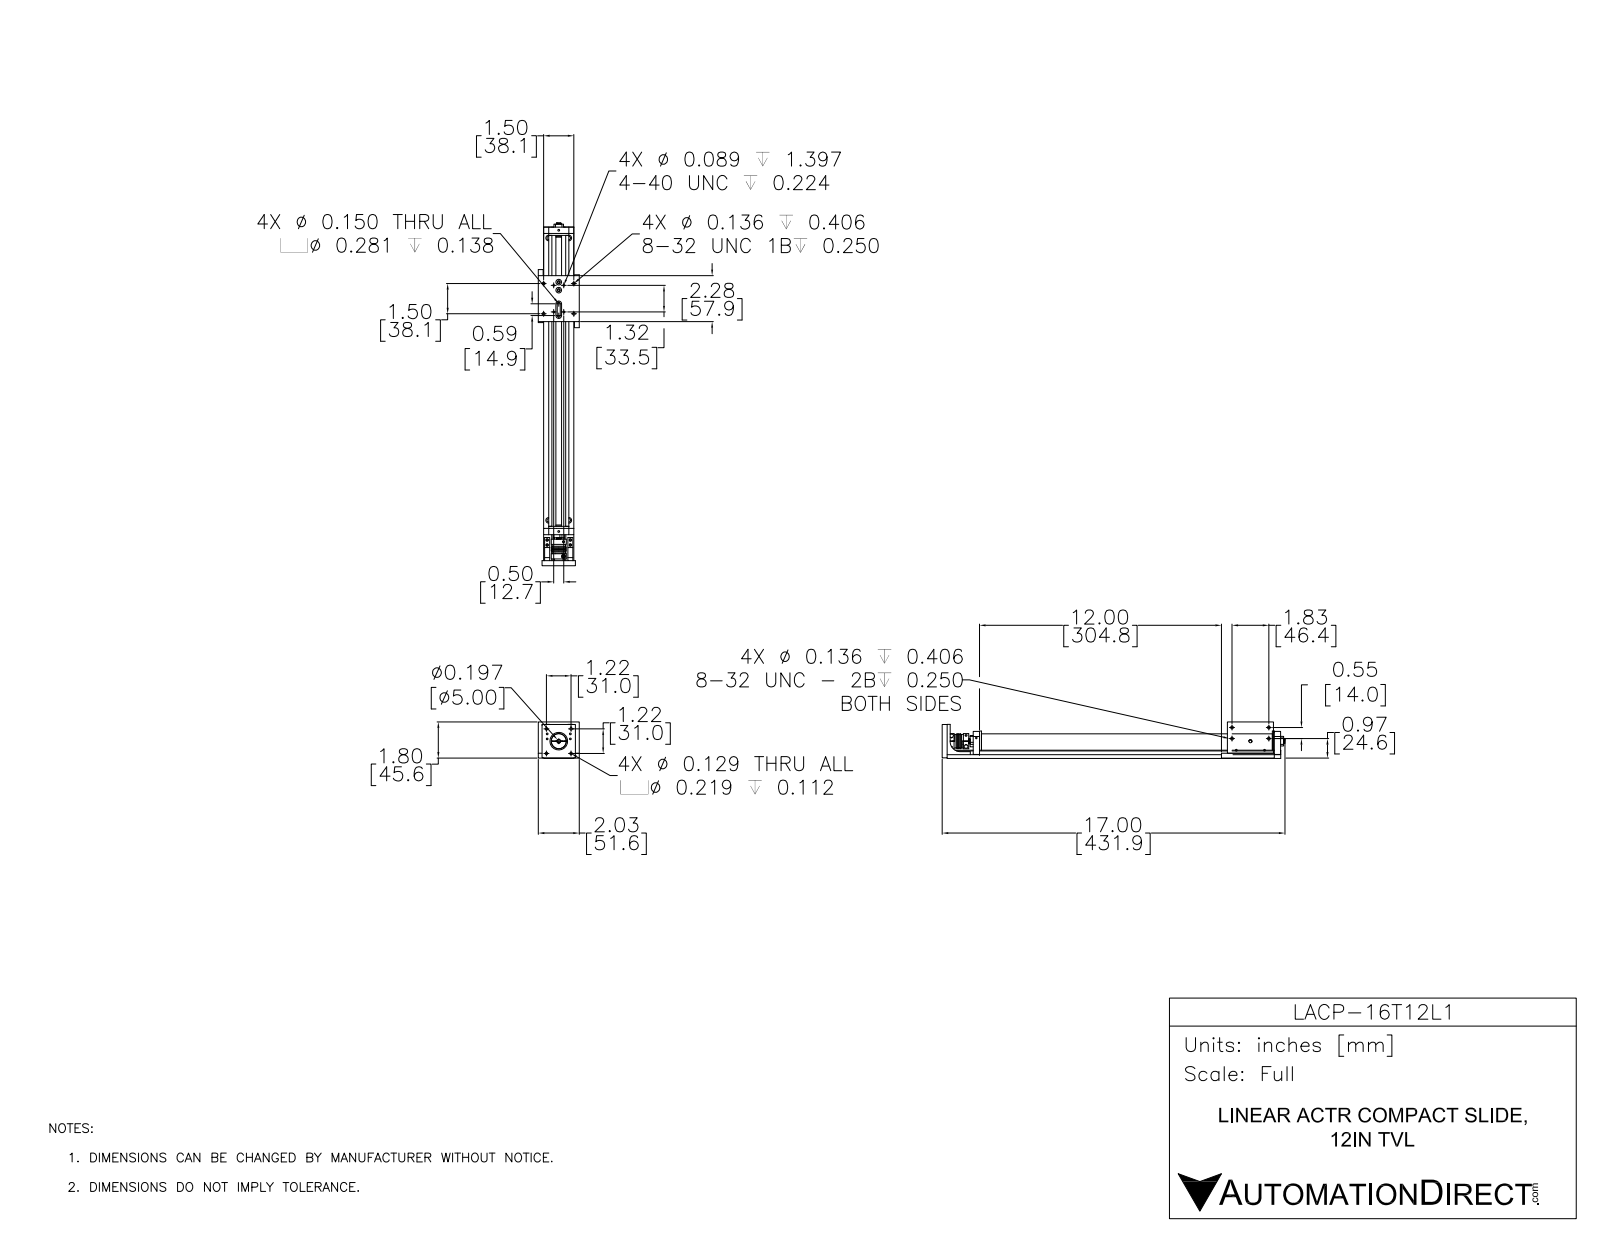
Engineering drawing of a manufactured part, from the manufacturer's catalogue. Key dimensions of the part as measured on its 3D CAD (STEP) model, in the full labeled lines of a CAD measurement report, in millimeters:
Part name (STEP PRODUCT): LACP-16T12L1; LACP-16TXXL1-CAR; LACP-16T12L1-RAIL
STEP written by: SolidWorks 2016 (AUTOMOTIVE_DESIGN)
Units: millimetres
Bodies: 25 solids, 827 faces (271 planar, 472 cylindrical, 84 other)
Overall size (bounding box): 431.7 × 51.6 × 46
Volume: 343 500 mm³ · Surface area: 154 600 mm²
Round holes (diameter × count): ⌀2.3 ×16, ⌀7.1 ×10, ⌀3.5 ×8, ⌀4.3 ×8, ⌀3.8 ×6, ⌀1.8 ×4, ⌀3.3 ×4, ⌀3.3 ×4, ⌀3.5 ×4, ⌀5.6 ×4, ⌀7.1 ×4, ⌀5 ×3
Round bosses / shafts (diameter × count): ⌀4 ×3, ⌀3.8 ×2, ⌀25.4 ×1, ⌀19 ×1, ⌀18 ×1, ⌀17.1 ×1, ⌀17 ×1, ⌀15 ×1
Partial cylindrical surfaces — rounded edges, fillets, slot ends (radius × count): R1.2 ×4, R1.6 ×4, R2.4 ×4, R3.2 ×3, R1.3 ×2, R1.9 ×2, R3.6 ×2, R6.4 ×2
Main face-to-face distances: 4.7, 6.7, 44.8, 31, 26.2, 6.4, 41.2, 46, 15.1, 51.6
Hole centre spacings: 102.4, 12.7, 101.6, 203.6, 38, 104.7, 203.2, 211.7
